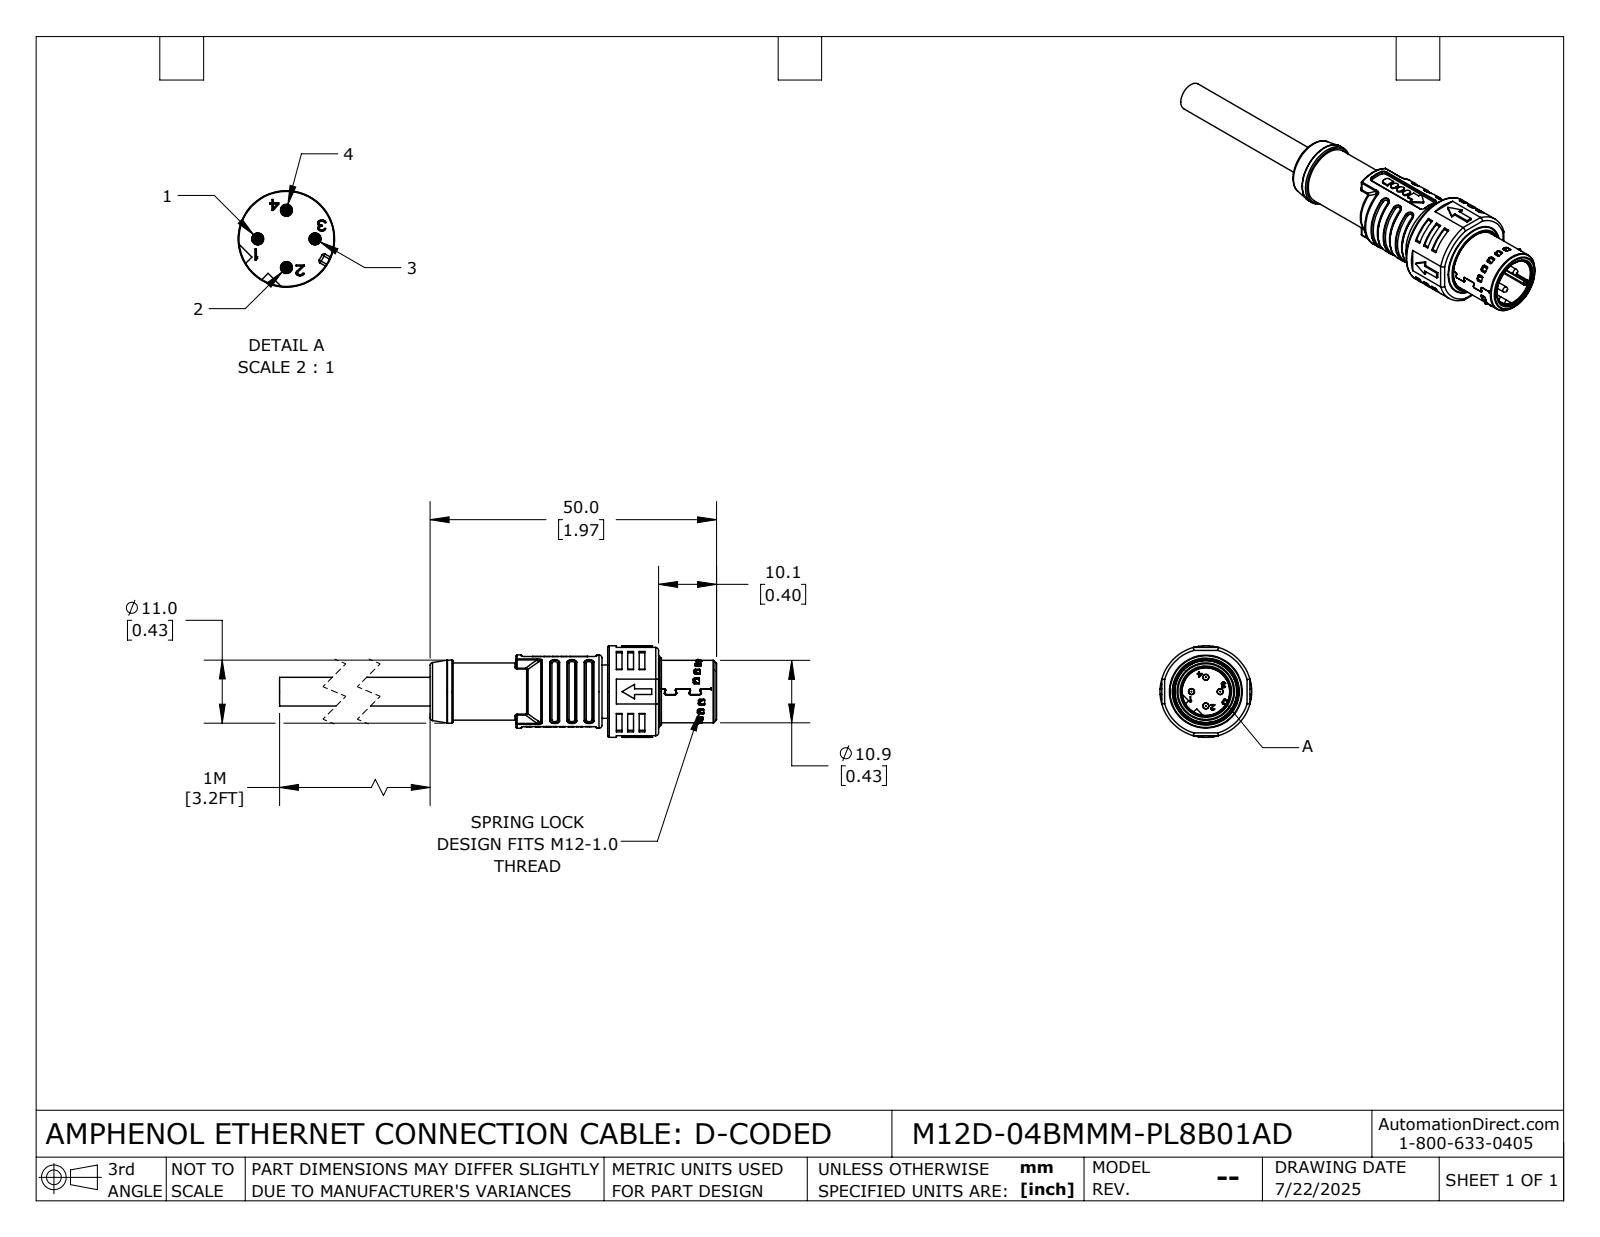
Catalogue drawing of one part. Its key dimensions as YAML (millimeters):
part_name: "M12D-04BMMM-PL8B01AD"
step_written_by: "SolidWorks 2024 (CONFIG_CONTROL_DESIGN)"
units: millimeters
bodies: {solids: 1, faces: 2139, planar: 996, cylindrical: 644, other: 499}
overall_size: [80, 16, 16]
volume: 5399
surface_area: 5961
round_holes:
  - {diameter: 1.05, count: 4}
  - {diameter: 8.3, count: 1}
  - {diameter: 9, count: 1}
  - {diameter: 10.15, count: 1}
  - {diameter: 10.5, count: 1}
  - {diameter: 10.9, count: 1}
  - {diameter: 11.5, count: 1}
  - {diameter: 11.8, count: 1}
  - {diameter: 14.2, count: 1}
round_bosses_or_shafts:
  - {diameter: 1, count: 4}
  - {diameter: 16, count: 1}
  - {diameter: 14.1, count: 1}
  - {diameter: 12.8, count: 1}
  - {diameter: 12.4, count: 1}
  - {diameter: 11, count: 1}
  - {diameter: 10.45, count: 1}
  - {diameter: 10.4, count: 1}
partial_cylinders:
  - {radius: 0.2, count: 119}
  - {radius: 0.25, count: 66}
  - {radius: 0.3, count: 64}
  - {radius: 0.15, count: 44}
  - {radius: 0.5, count: 38}
  - {radius: 0.13, count: 12}
  - {radius: 0.7, count: 11}
  - {radius: 0.1, count: 7}
face_to_face_distances: [1, 30, 10.1, 8.9, 2.5, 1.2, 8.6, 32.5, 15.4, 1.5]
hole_center_spacings: [2.5, 3.54, 5]
